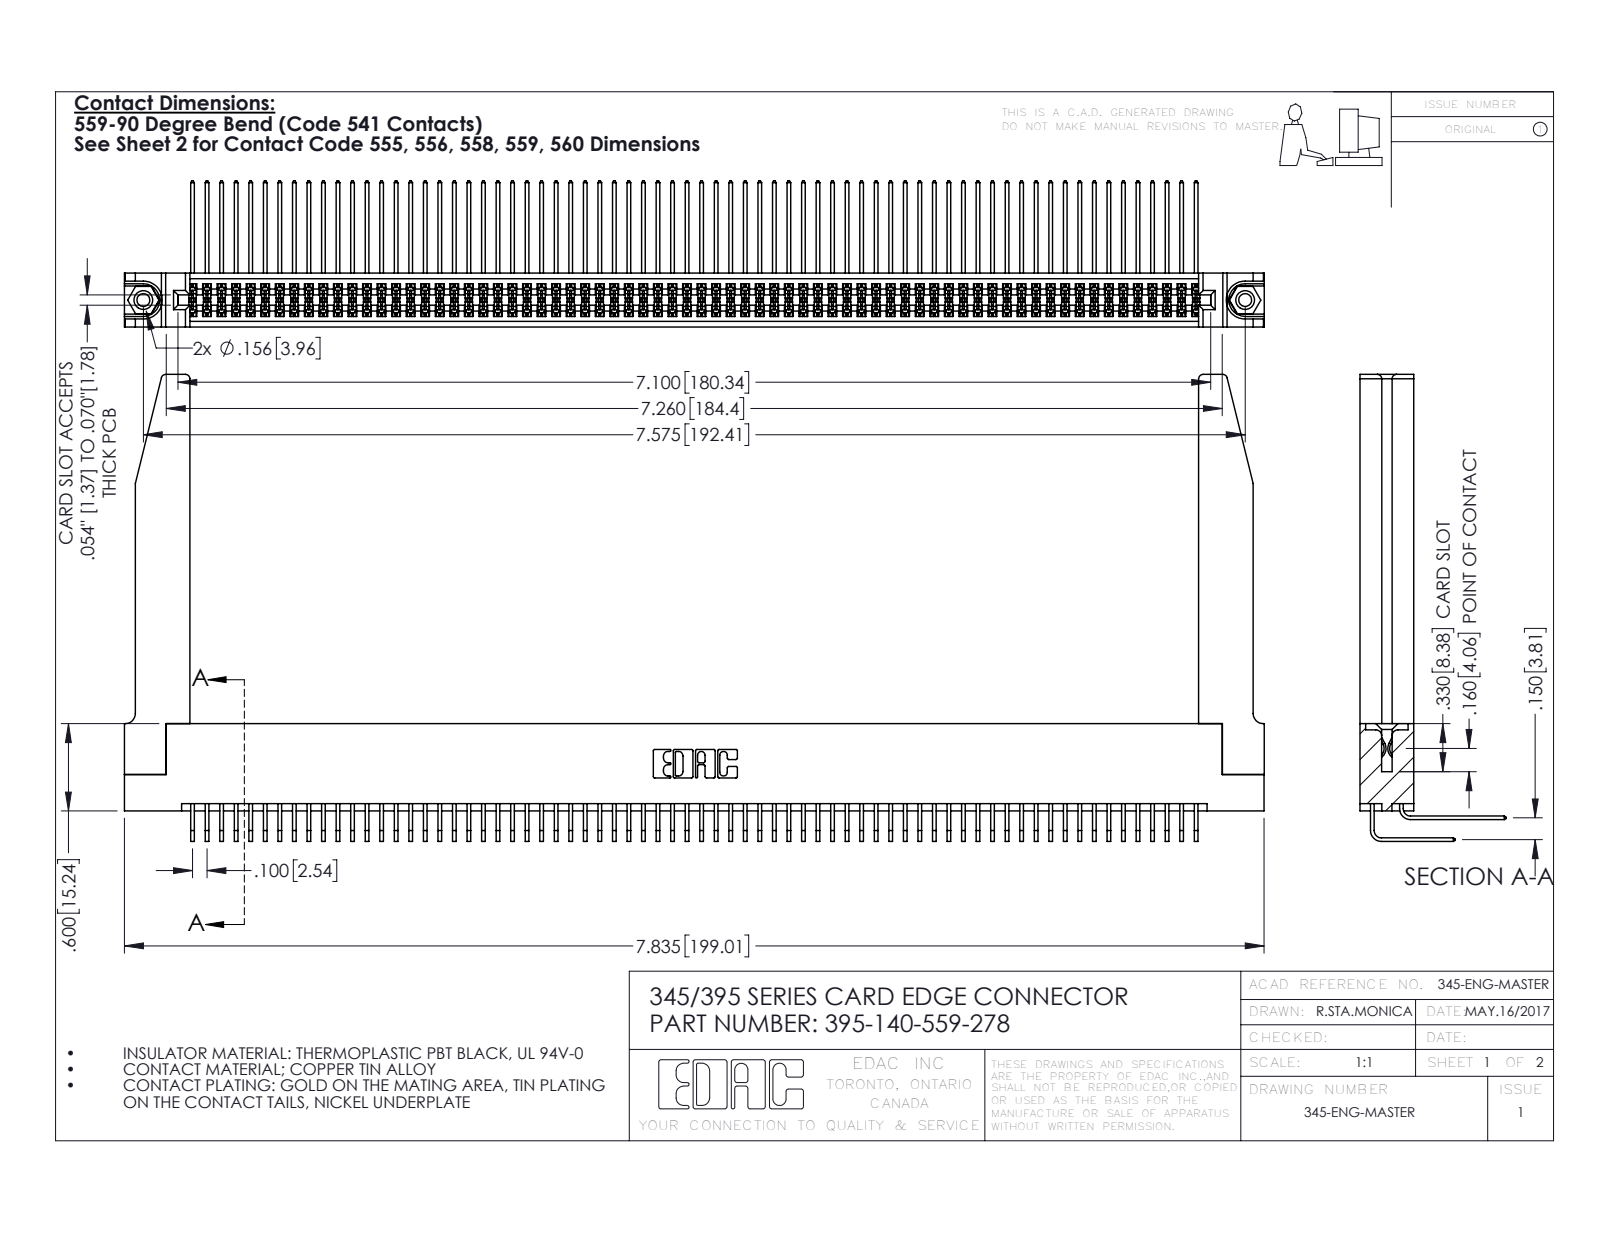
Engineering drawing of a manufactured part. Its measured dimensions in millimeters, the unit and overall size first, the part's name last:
Units: millimetres
Overall size (bounding box): 199 × 81.5 × 25.5
Round holes (diameter × count): ⌀2.3 ×2, ⌀3.2 ×2, ⌀4 ×2, ⌀1.6 ×1
Round bosses / shafts (diameter × count): ⌀3.9 ×2
Partial cylindrical surfaces — rounded edges, fillets, slot ends (radius × count): R0.2 ×279, R0.3 ×22, R0.8 ×8, R0.2 ×6, R0.8 ×6, R0.7 ×3, R0.4 ×2, R0.5 ×2
Main face-to-face distances: 1.8, 7.6, 9.4, 5.1, 2.5, 6.9, 0.6, 5.7, 4.4, 3.8
Hole centre spacings: 6.9, 186.4, 192.4
Volume: 28 170 mm³ · Surface area: 41 340 mm²
Bodies: 145 solids, 7640 faces (5122 planar, 2466 cylindrical, 52 other)
Part name (STEP PRODUCT): 345-250-001_345-250-001-102; 345-220-078_345-220-078; 345-292-001_559 Tail - 2; 345-292-001_558 559 Tail - 1 (+2 more)
STEP written by: SolidWorks 2016 (CONFIG_CONTROL_DESIGN)
